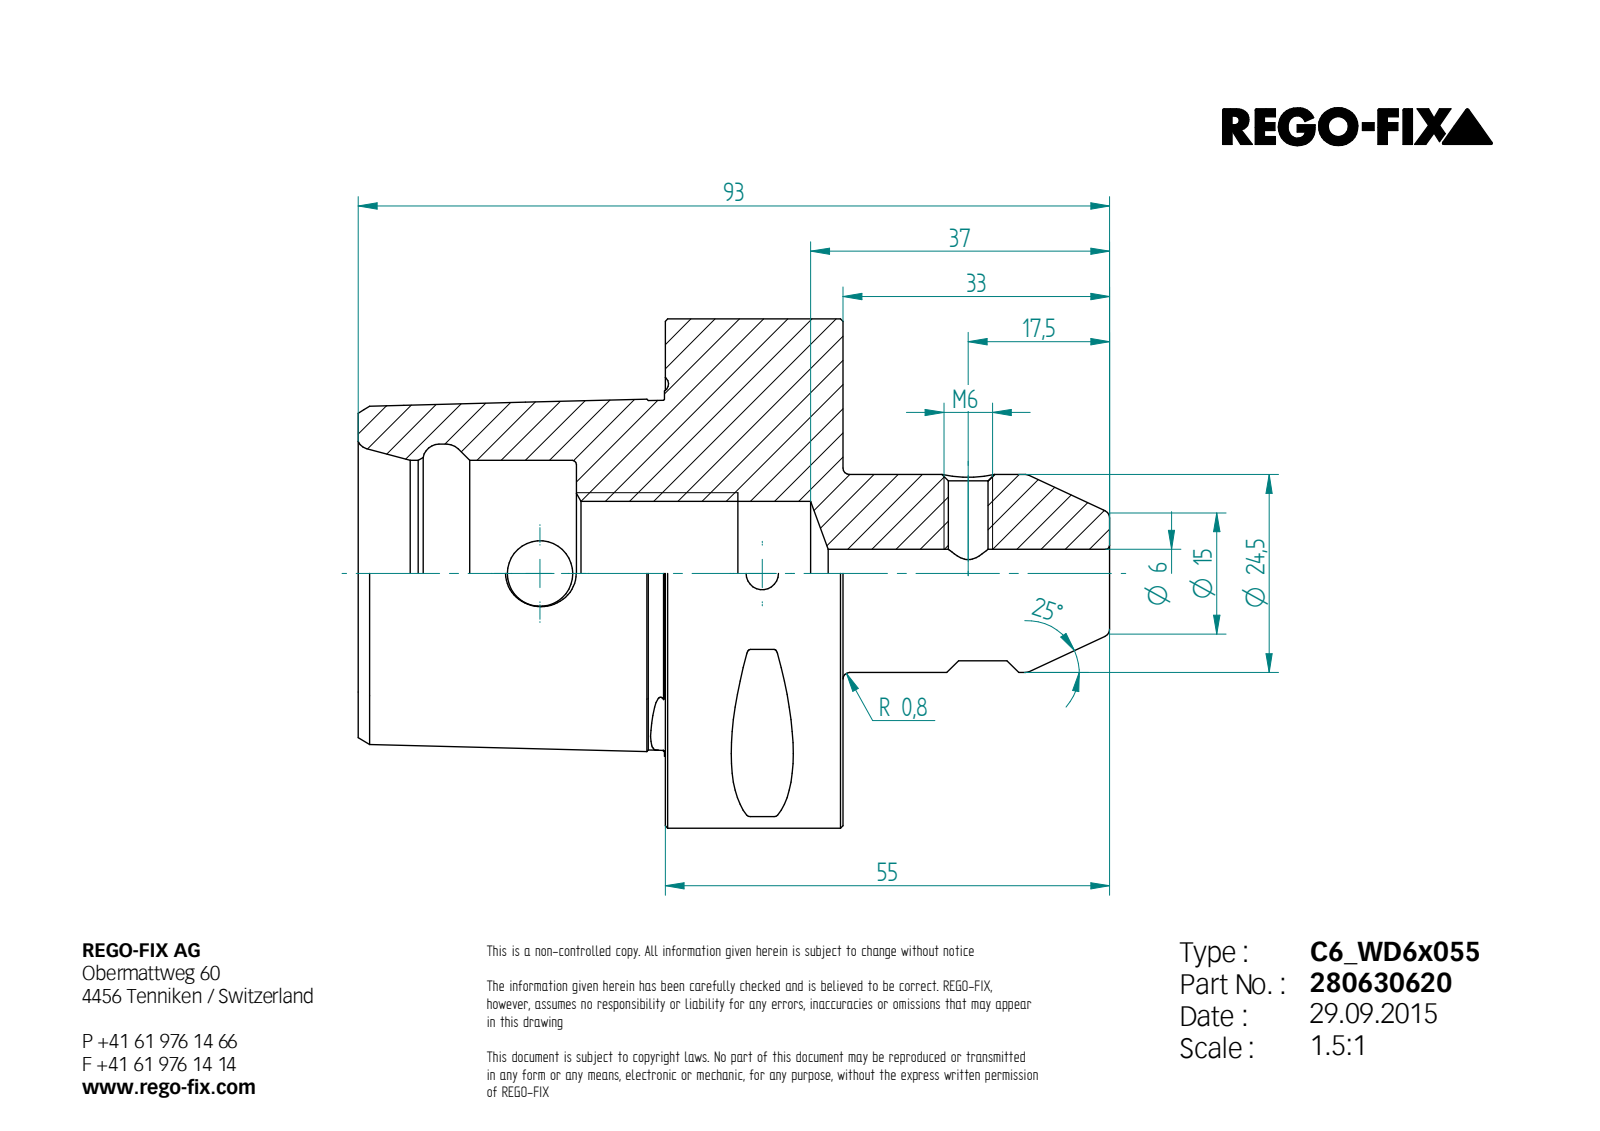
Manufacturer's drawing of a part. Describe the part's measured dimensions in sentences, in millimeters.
Its 3-D file was written by "Unknown (AUTOMOTIVE_DESIGN)". It is 1 solid with 108 faces: 23 planar, 20 cylindrical and 65 other. Overall it measures 93 by 63 by 63 millimeters. Its volume is 108 111 cubic millimeters and its surface area 22 923 square millimeters. Round holes: 1 of diameter 4, 1 of diameter 4.92, 1 of diameter 6, 1 of diameter 8.1, 1 of diameter 17.84, 1 of diameter 28, 1 of diameter 32. Round bosses or shafts: 1 of diameter 63, 1 of diameter 24.5. Partial cylindrical surfaces (rounded edges, fillets, slot ends): 8 of radius 0.5. The main face-to-face distances are 22, 38, 60, 33, 24.89, 27, 11, 55.8, 37.9, 10.9. The hole center spacings are 27.5.
